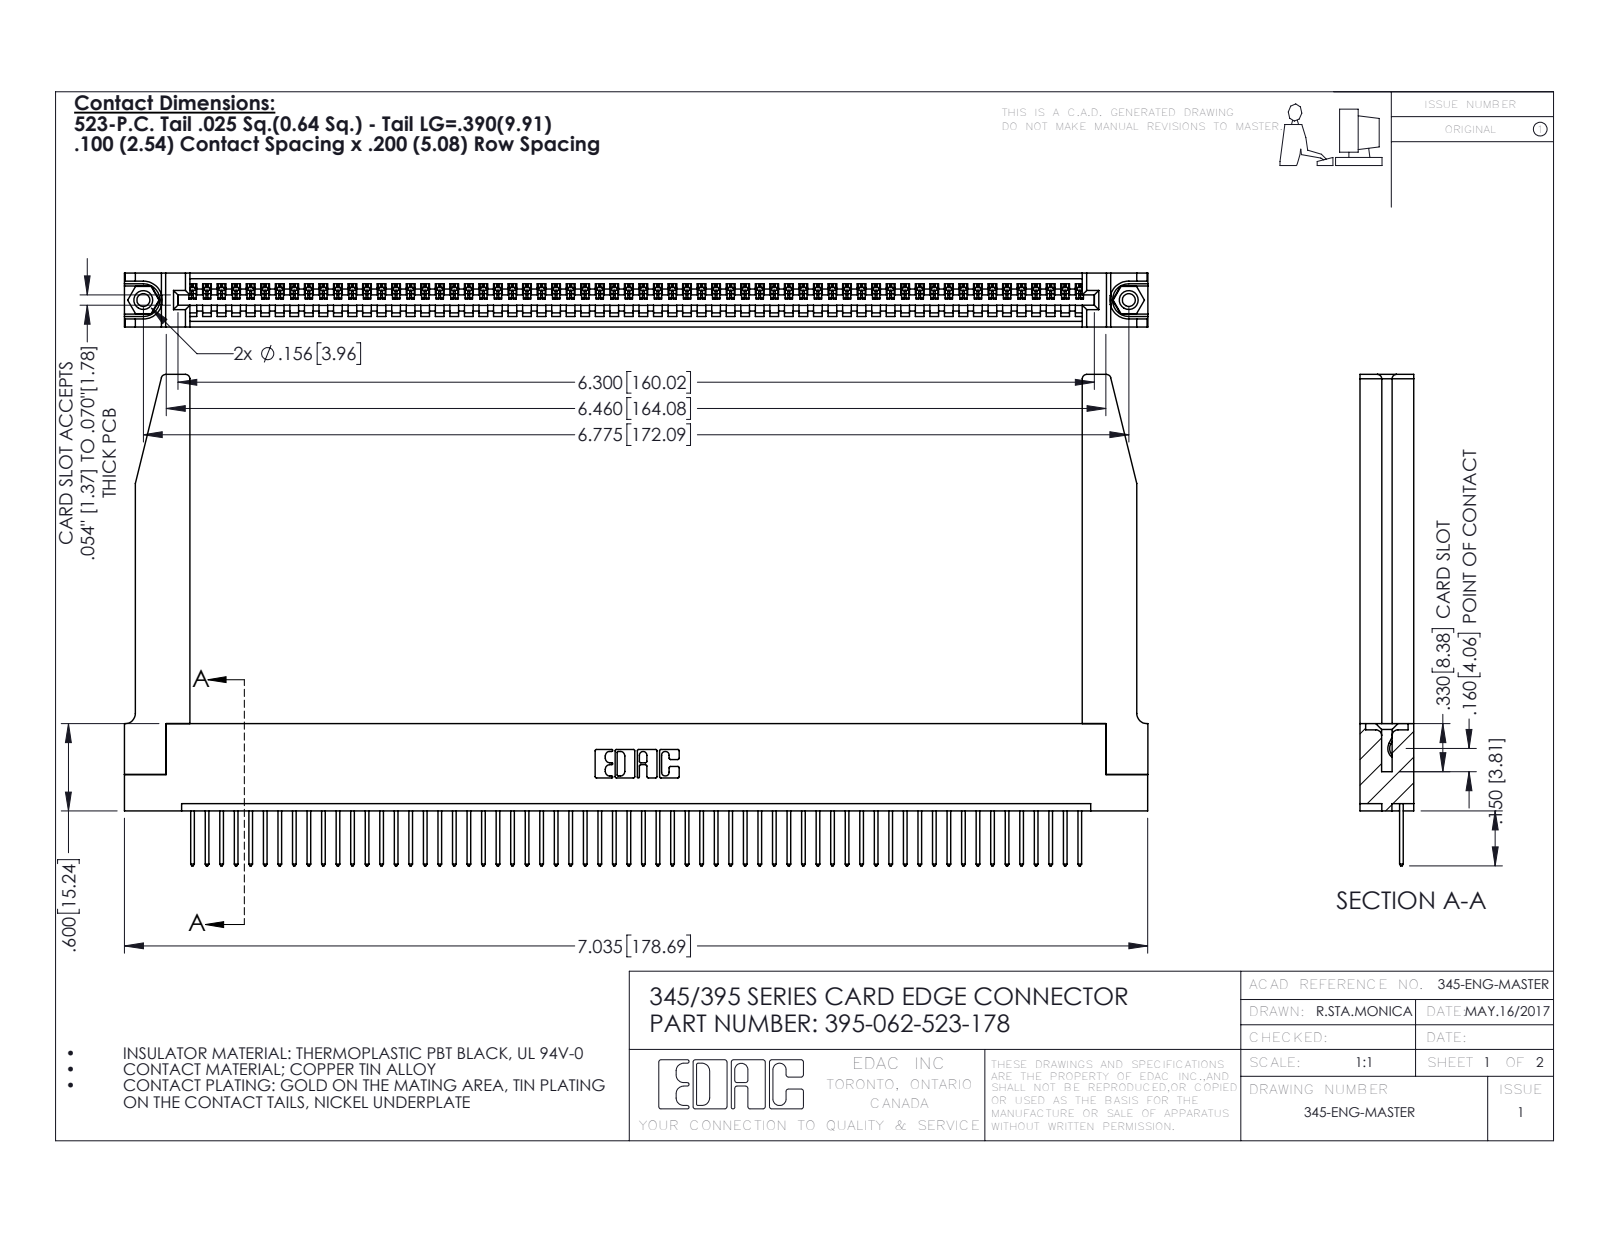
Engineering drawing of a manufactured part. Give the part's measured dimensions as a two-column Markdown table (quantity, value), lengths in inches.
| quantity | value |
| --- | --- |
| part name | 345-292-001_345-293-123; 345 Part_Flush Mounting Lugs - 0.156 Dia-TH; 345-220-078_345-220-078; 395-062-523-178 (+1 more) |
| STEP written by | SolidWorks 2016 (CONFIG_CONTROL_DESIGN) |
| units | inches |
| bodies | 67 solids, 3956 faces (2702 planar, 1202 cylindrical, 52 other) |
| overall size | 7.036 × 3.377 × 0.37 |
| volume | 1.519 in³ |
| surface area | 46.39 in² |
| round holes (diameter × count) | 0.089 × 2, 0.125 × 2, 0.156 × 2, 0.064 × 1 |
| round bosses / shafts (diameter × count) | 0.155 × 2 |
| partial cylindrical surfaces (radius × count) | 0.006 × 124, 0.01 × 124, 0.01 × 22, 0.03 × 8, 0.007 × 6, 0.031 × 6, 0.026 × 3, 0.031 × 2 |
| main face-to-face distances | 0.072, 0.37, 0.298, 0.2, 0.098, 0.272, 0.025, 0.225, 0.148, 0.15 |
| hole center spacings | 0.27, 6.539, 6.775 |
